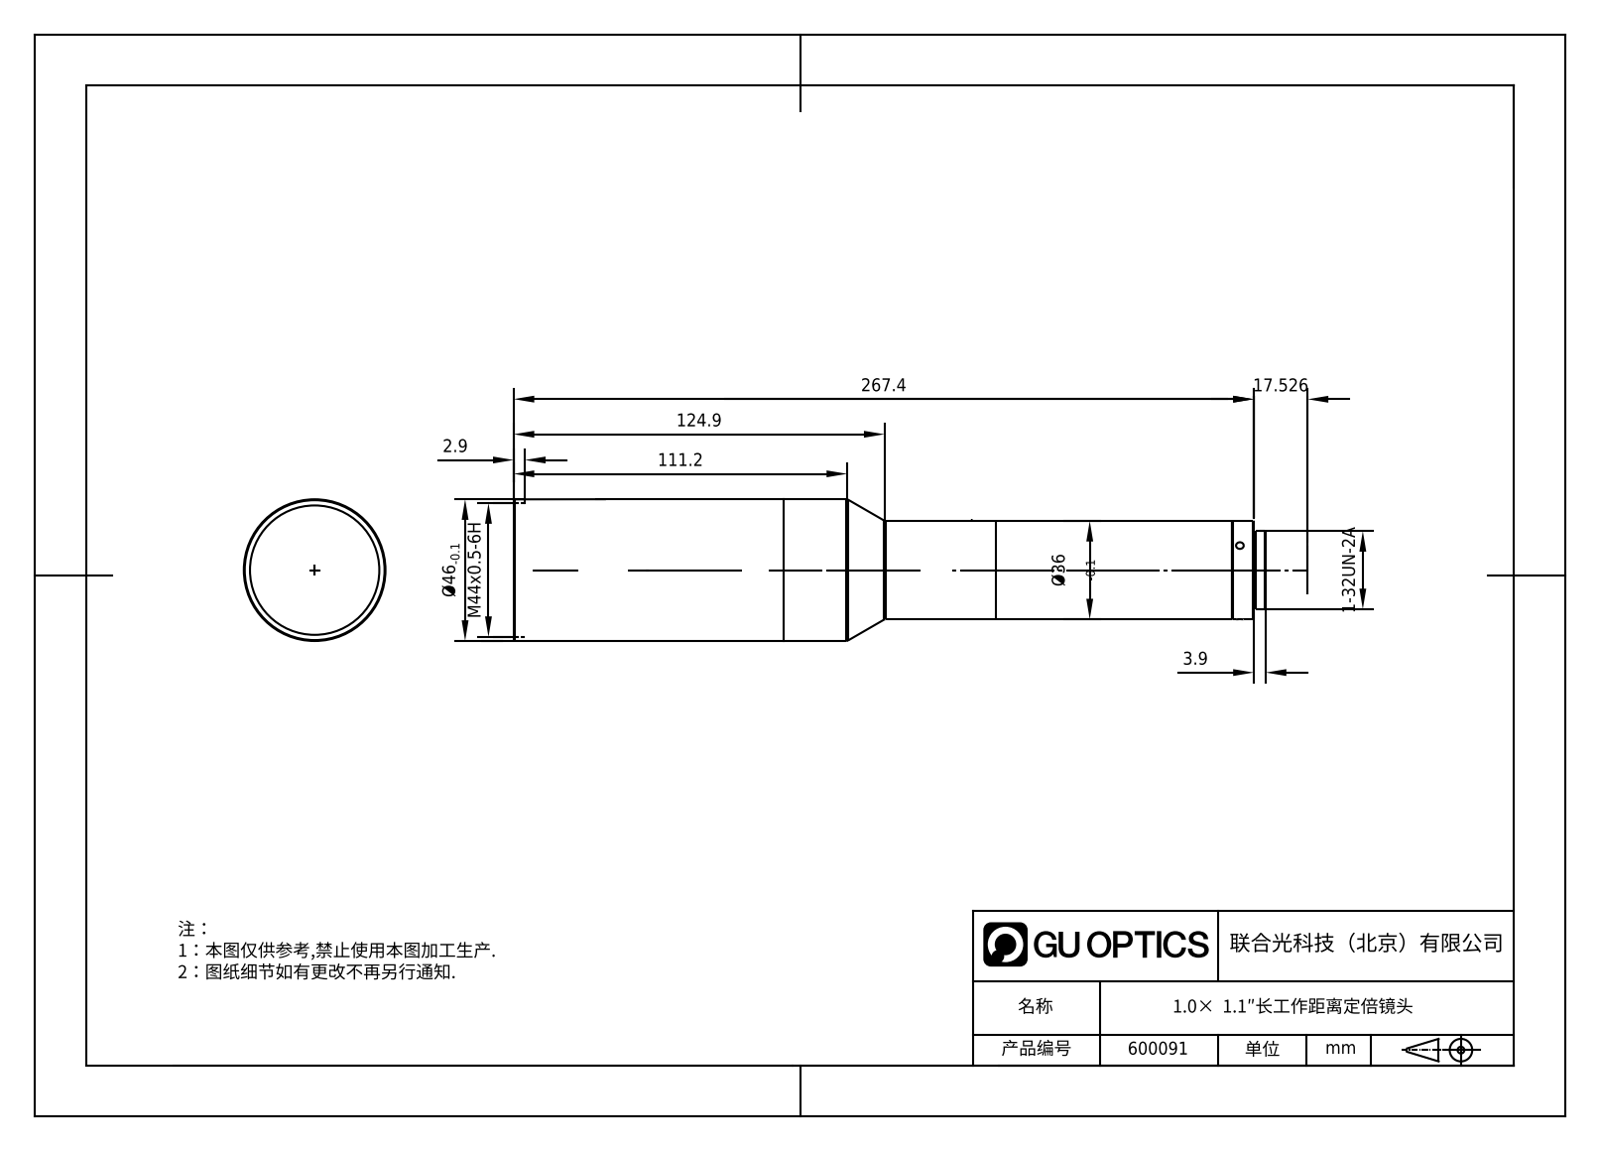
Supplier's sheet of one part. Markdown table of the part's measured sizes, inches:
| quantity | value |
| --- | --- |
| part name | 600091 |
| STEP written by | SolidWorks 2020 (CONFIG_CONTROL_DESIGN) |
| units | inches |
| bodies | 2 solids, 37 faces (10 planar, 11 cylindrical, 16 other) |
| overall size | 10.684 × 1.811 × 1.811 |
| volume | 19.89 in³ |
| surface area | 62.63 in² |
| round holes (diameter × count) | 0.098 × 3, 1.654 × 1, 1.744 × 1 |
| round bosses / shafts (diameter × count) | 1.811 × 1, 1.26 × 1, 1 × 1, 0.969 × 1 |
| main face-to-face distances | 10.181, 0.35, 10.531, 10.685, 10.334, 0.154, 3.465, 3.115, 7.066, 7.219 |
